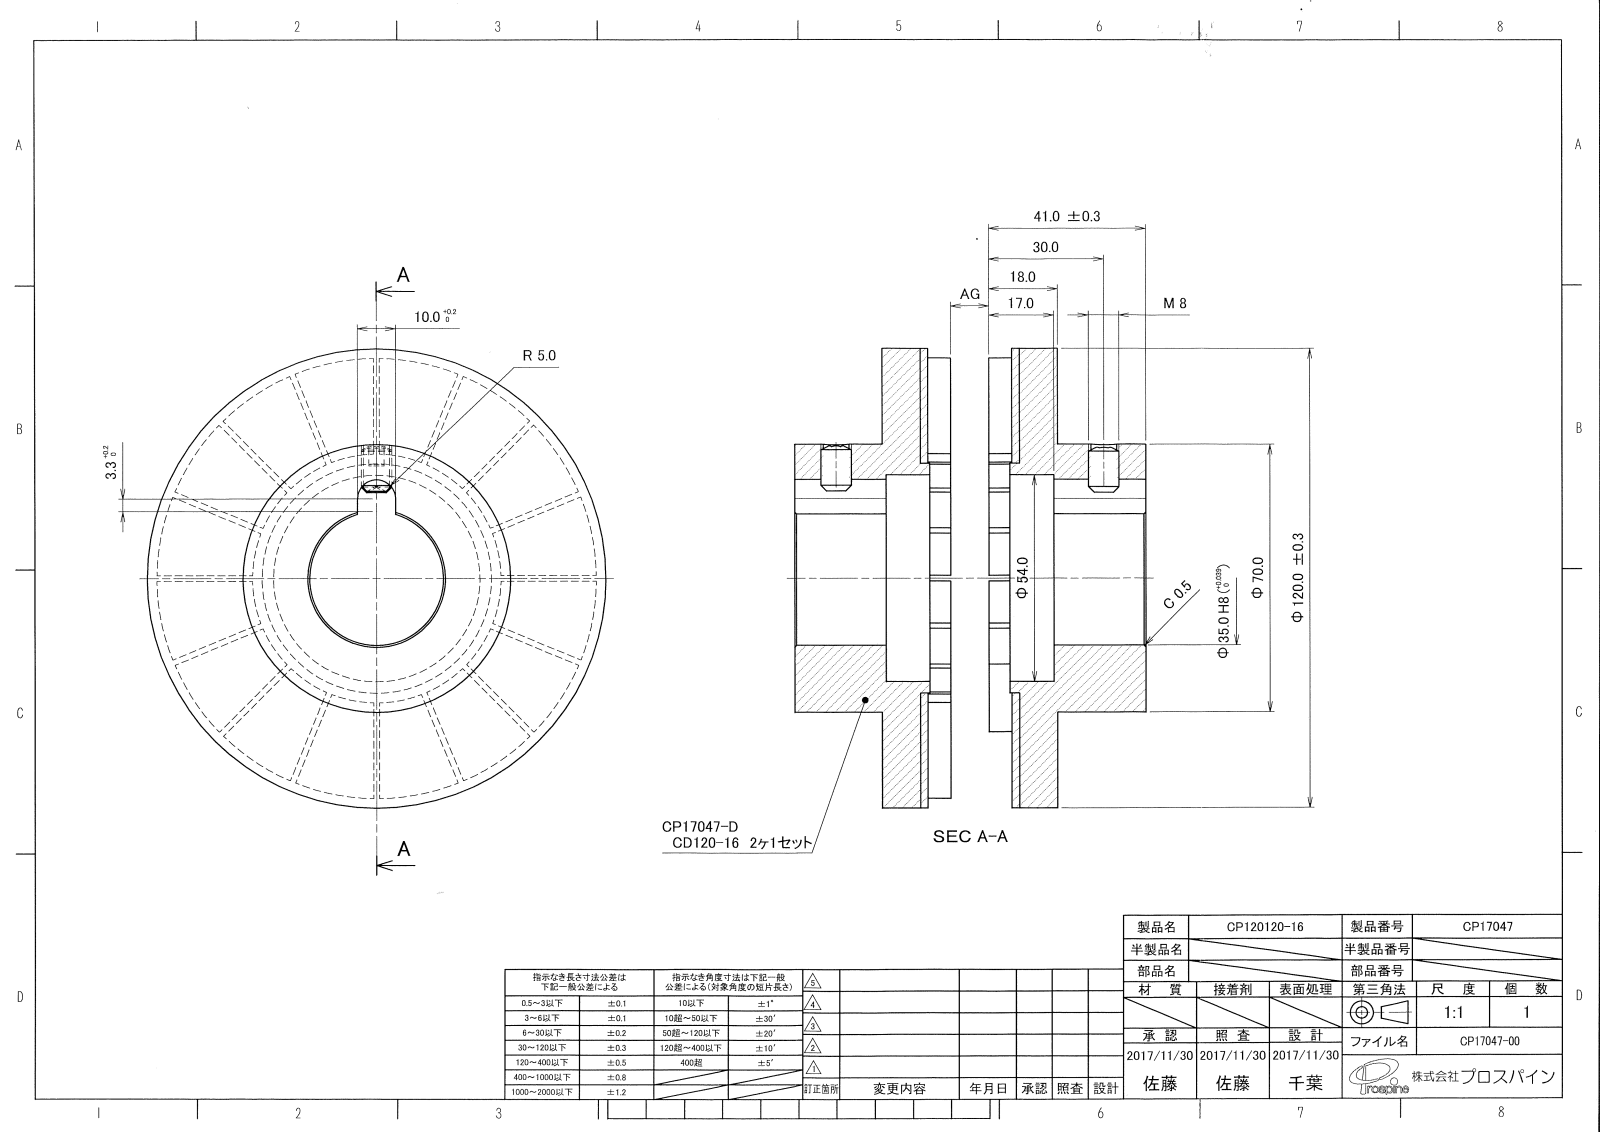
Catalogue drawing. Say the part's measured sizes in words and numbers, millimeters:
Its 3-D file was written by "PSStep 10.0 (CONFIG_CONTROL_DESIGN)". It is 21 solids with 207 faces: 123 planar, 77 cylindrical and 7 other. Overall it measures 120 by 120 by 41 millimeters. Its volume is 217 058 cubic millimeters and its surface area 68 441 square millimeters. Round holes: 1 of diameter 6.75, 1 of diameter 35, 1 of diameter 54, 1 of diameter 60, 1 of diameter 65. Round bosses or shafts: 1 of diameter 120, 1 of diameter 115, 1 of diameter 70, 1 of diameter 8. Partial cylindrical surfaces (rounded edges, fillets, slot ends): 1 of radius 5. The main face-to-face distances are 10, 8, 18, 1.5, 41, 33, 23, 6, 2, 12.
